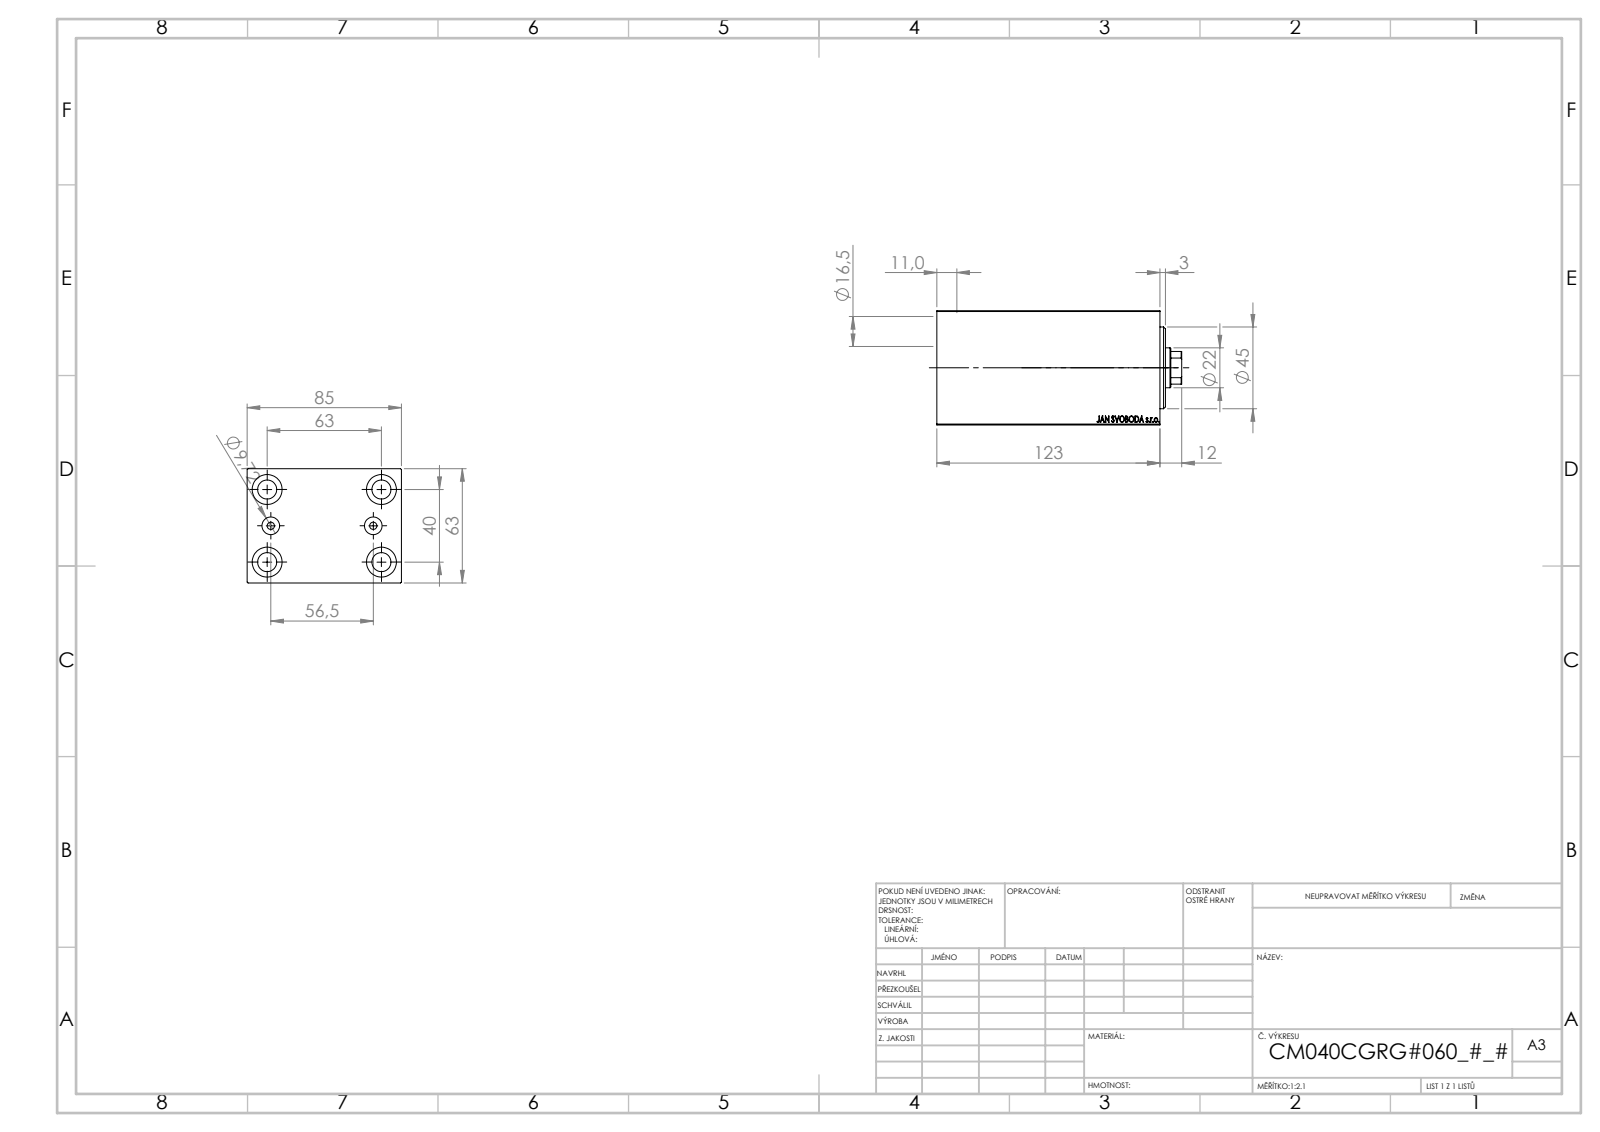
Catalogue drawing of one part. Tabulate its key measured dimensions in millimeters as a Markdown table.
| quantity | value |
| --- | --- |
| part name | V450CM_C_VCP; V450CM_VC_B; V450CM_C_Body |
| STEP written by | SolidWorks 2019 (CONFIG_CONTROL_DESIGN) |
| units | millimeters |
| bodies | 3 solids, 858 faces (408 planar, 56 cylindrical, 394 other) |
| overall size | 135 × 85 × 63 |
| volume | 552 886 mm³ |
| surface area | 94 982 mm² |
| round holes (diameter × count) | 10.5 × 4, 16.5 × 4, 4 × 2, 9.72 × 2, 12.5 × 1, 22 × 1, 25.5 × 1, 40 × 1, 42 × 1, 45 × 1 |
| partial cylindrical surfaces (radius × count) | 10.5 × 1 |
| main face-to-face distances | 63, 85, 123, 88.25, 34.75, 10, 113, 78.25, 11, 112 |
| hole center spacings | 20.26, 37.31, 63.01, 28.25, 40, 63, 74.63, 56.5 |
